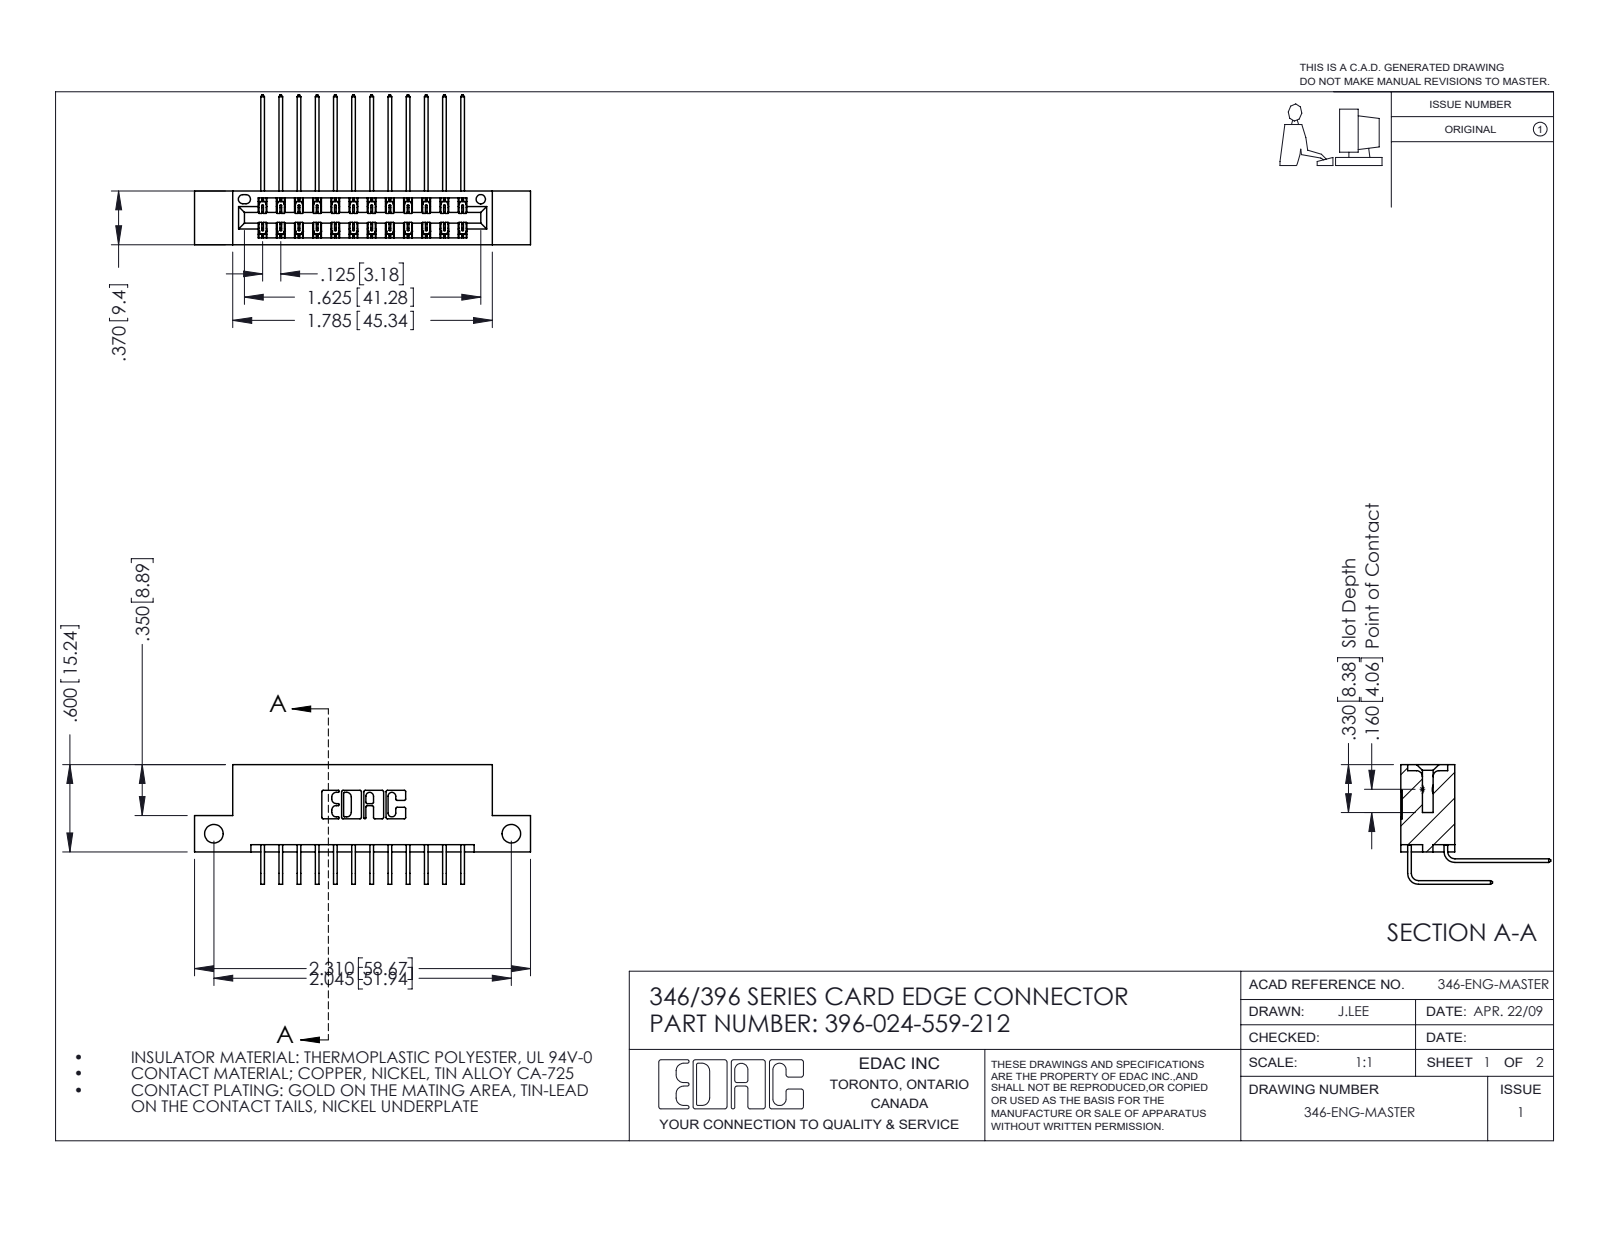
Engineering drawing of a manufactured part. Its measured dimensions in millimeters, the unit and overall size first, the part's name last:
Units: millimetres
Overall size (bounding box): 58.7 × 26.2 × 20.9
Round holes (diameter × count): ⌀3.3 ×2, ⌀1.6 ×1
Partial cylindrical surfaces — rounded edges, fillets, slot ends (radius × count): R0.2 ×36, R0.3 ×22, R0.2 ×6, R0.8 ×6, R0.7 ×3, R0.4 ×2, R0.6 ×2, R0.6 ×2
Main face-to-face distances: 1.2, 8.2, 6.4, 9.4, 0.6, 7.6, 1.8, 7, 3.8, 5.6
Hole centre spacings: 51.9
Volume: 5 540 mm³ · Surface area: 7 671 mm²
Bodies: 25 solids, 1418 faces (964 planar, 454 cylindrical, 0 other)
Part name (STEP PRODUCT): 346 Part_Flush Mounting Lugs - Side Mount; 345-292-001_559 Tail - 2; 396-024-559-212; 345-292-001_558 559 Tail - 1
STEP written by: SolidWorks 2016 (CONFIG_CONTROL_DESIGN)
